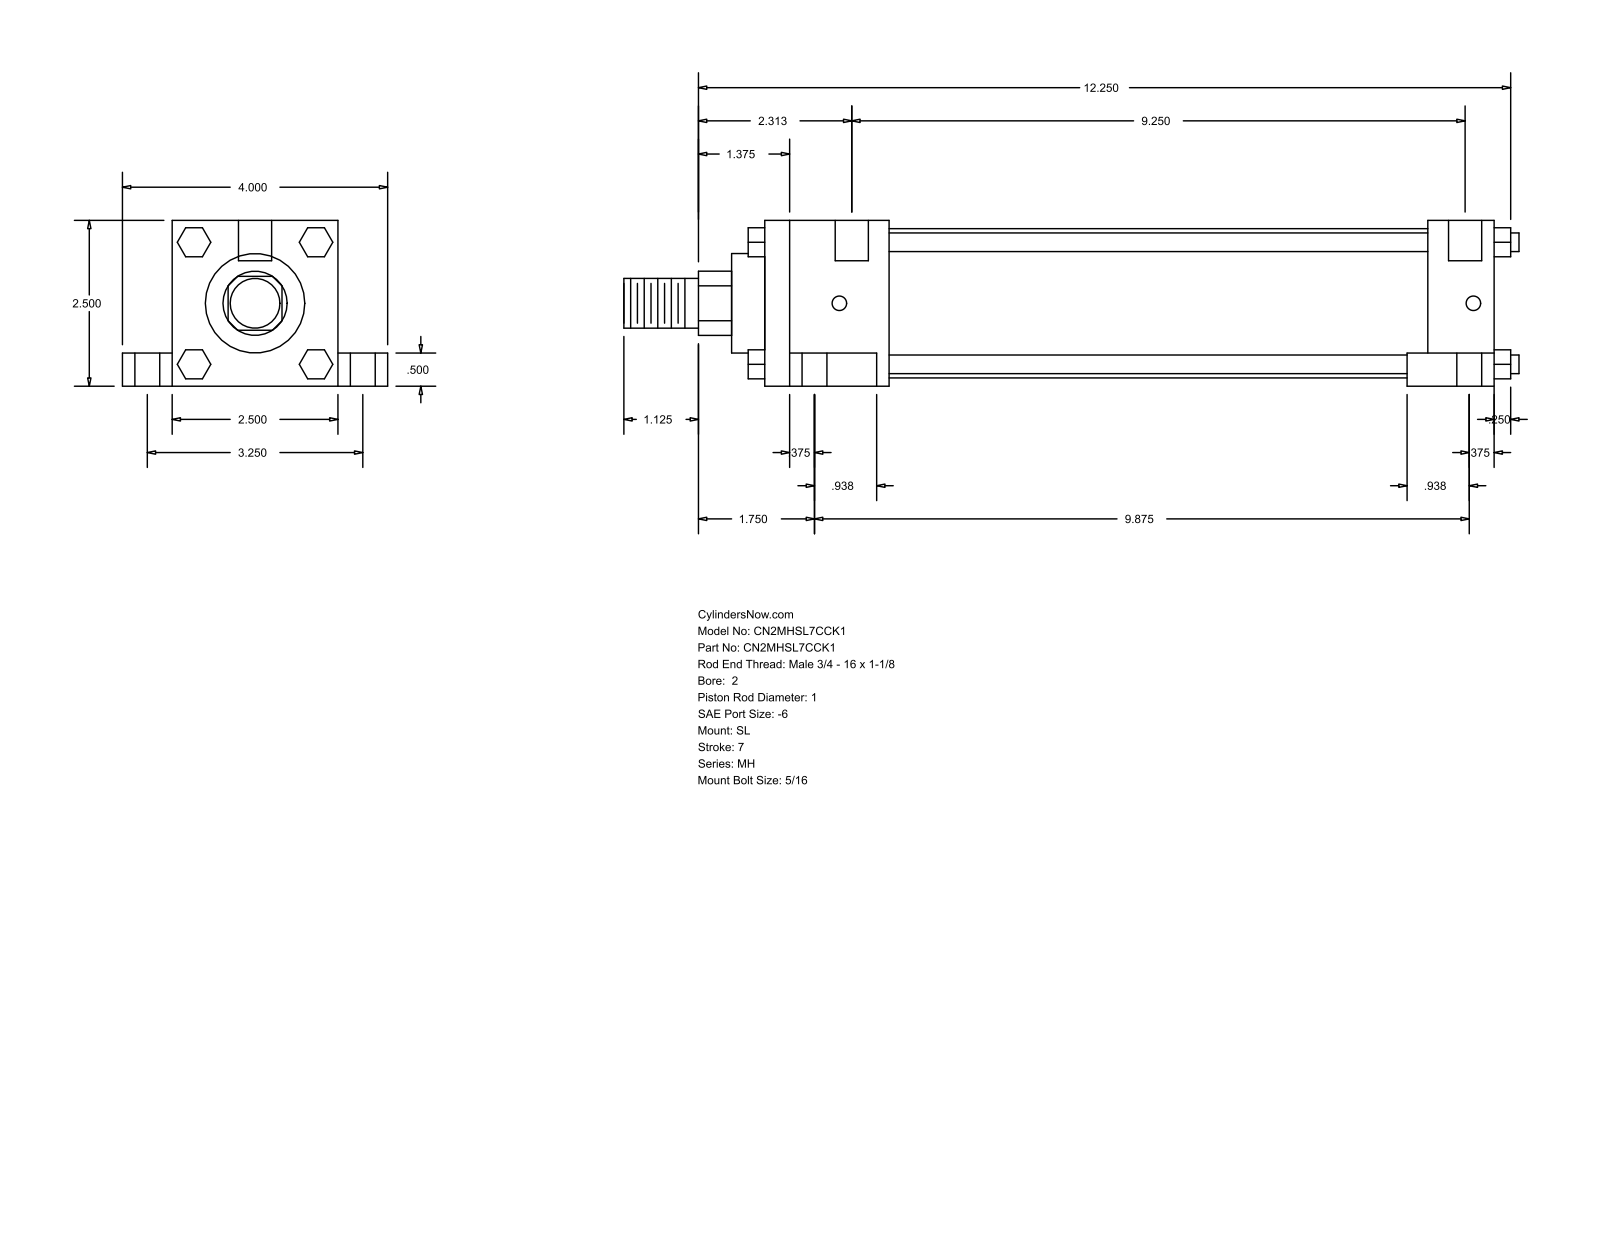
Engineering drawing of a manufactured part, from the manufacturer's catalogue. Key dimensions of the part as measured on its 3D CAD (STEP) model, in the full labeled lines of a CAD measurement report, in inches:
Part name (STEP PRODUCT): MH_SL__0200_1
STEP written by: GSSL Pune (CONFIG_CONTROL_DESIGN)
Units: inches
Bodies: 0 solids, 148 faces (112 planar, 36 cylindrical, 0 other)
Overall size (bounding box): 13.5 × 4 × 2.5
Round holes (diameter × count): ⌀0.219 ×4, ⌀0.375 ×4, ⌀0.625 ×4, ⌀0.5 ×2
Round bosses / shafts (diameter × count): ⌀0.281 ×4, ⌀2.25 ×1, ⌀1.5 ×1, ⌀1 ×1, ⌀0.75 ×1
Partial cylindrical surfaces — rounded edges, fillets, slot ends (radius × count): R0.484 ×1
Main face-to-face distances: 2.5, 11, 0.5, 0.75, 2, 3.25, 1, 10, 1.875, 8.125
Hole centre spacings: 1.626, 1.668, 1.719, 3.25, 9.453, 9.562, 9.637, 9.875
